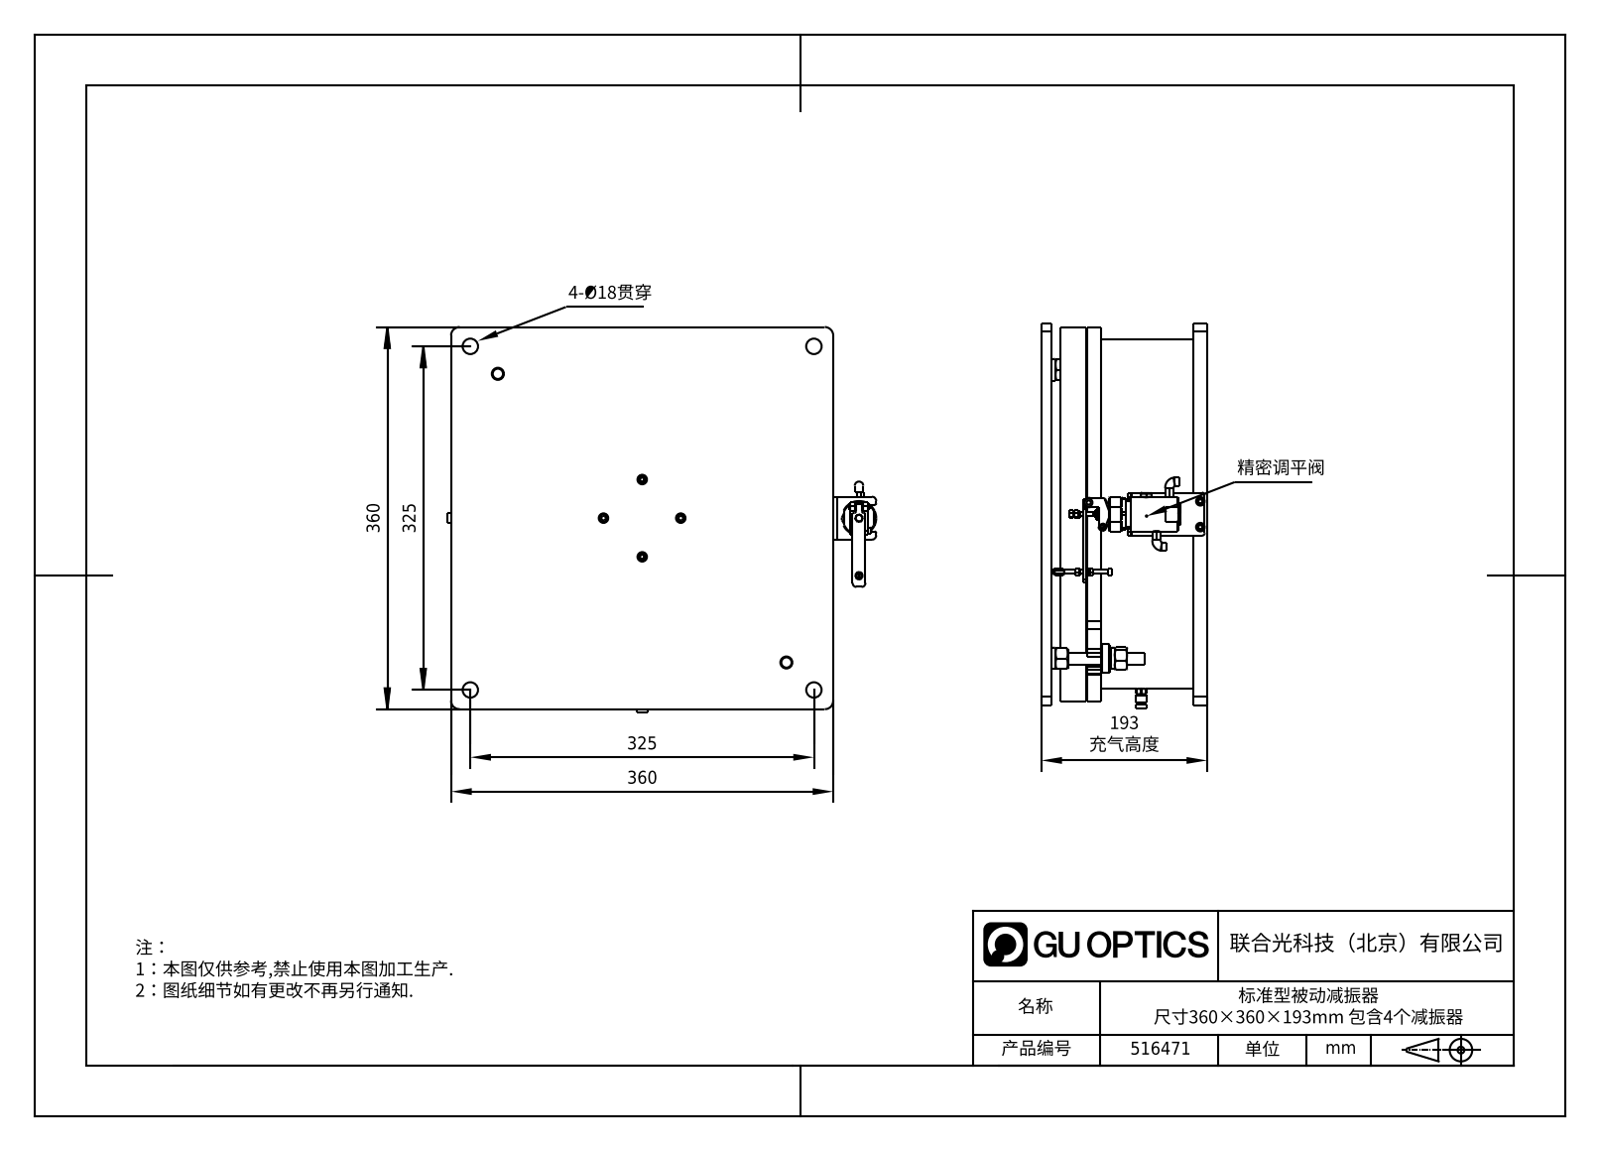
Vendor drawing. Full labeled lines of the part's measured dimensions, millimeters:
Part name (STEP PRODUCT): 516471
STEP written by: SolidWorks 2020 (CONFIG_CONTROL_DESIGN)
Units: millimetres
Bodies: 0 solids, 472 faces (264 planar, 139 cylindrical, 69 other)
Overall size (bounding box): 412.75 × 362.75 × 193
Round holes (diameter × count): ⌀18 ×6, ⌀9.7 ×3, ⌀5 ×1, ⌀11.5 ×1, ⌀13 ×1, ⌀25.1 ×1, ⌀343 ×1
Round bosses / shafts (diameter × count): ⌀11 ×5, ⌀12.7 ×3, ⌀12.6 ×3, ⌀12 ×3, ⌀10.4 ×3, ⌀10 ×3, ⌀8.45 ×3, ⌀8.1 ×3
Partial cylindrical surfaces — rounded edges, fillets, slot ends (radius × count): R5 ×10, R10 ×8, R2 ×3, R7 ×3, R0.3 ×2, R3 ×2, R4.5 ×2, R11 ×2
Main face-to-face distances: 16, 12, 193, 177, 181, 165, 124, 57, 108, 69
Hole centre spacings: 229.81, 299.22, 325, 38.18, 169.3, 191.63, 406.4, 421.44
